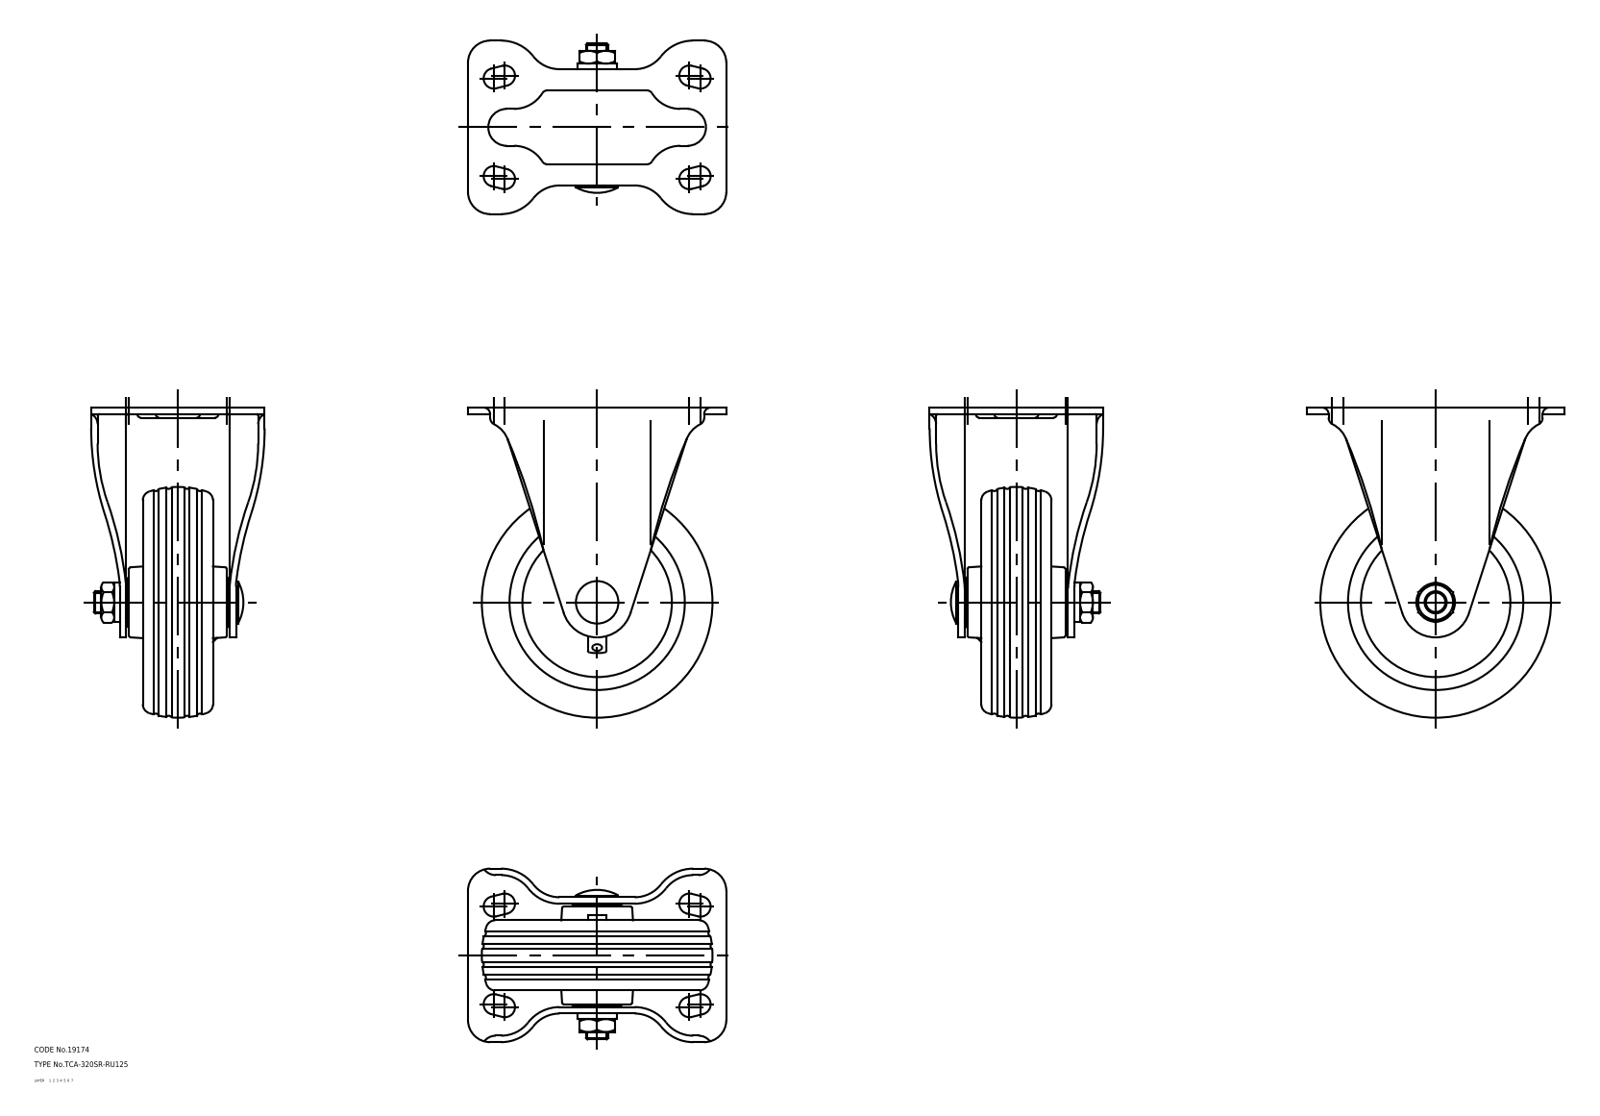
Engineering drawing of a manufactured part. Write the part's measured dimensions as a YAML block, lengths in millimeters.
part_name: "67124969; 67124982; 67124995"
step_written_by: "CADfix (AUTOMOTIVE_DESIGN)"
units: millimeters
bodies: {solids: 3, faces: 254, planar: 0, cylindrical: 0, other: 254}
overall_size: [168, 140, 94]
volume: 486031
surface_area: 110724
